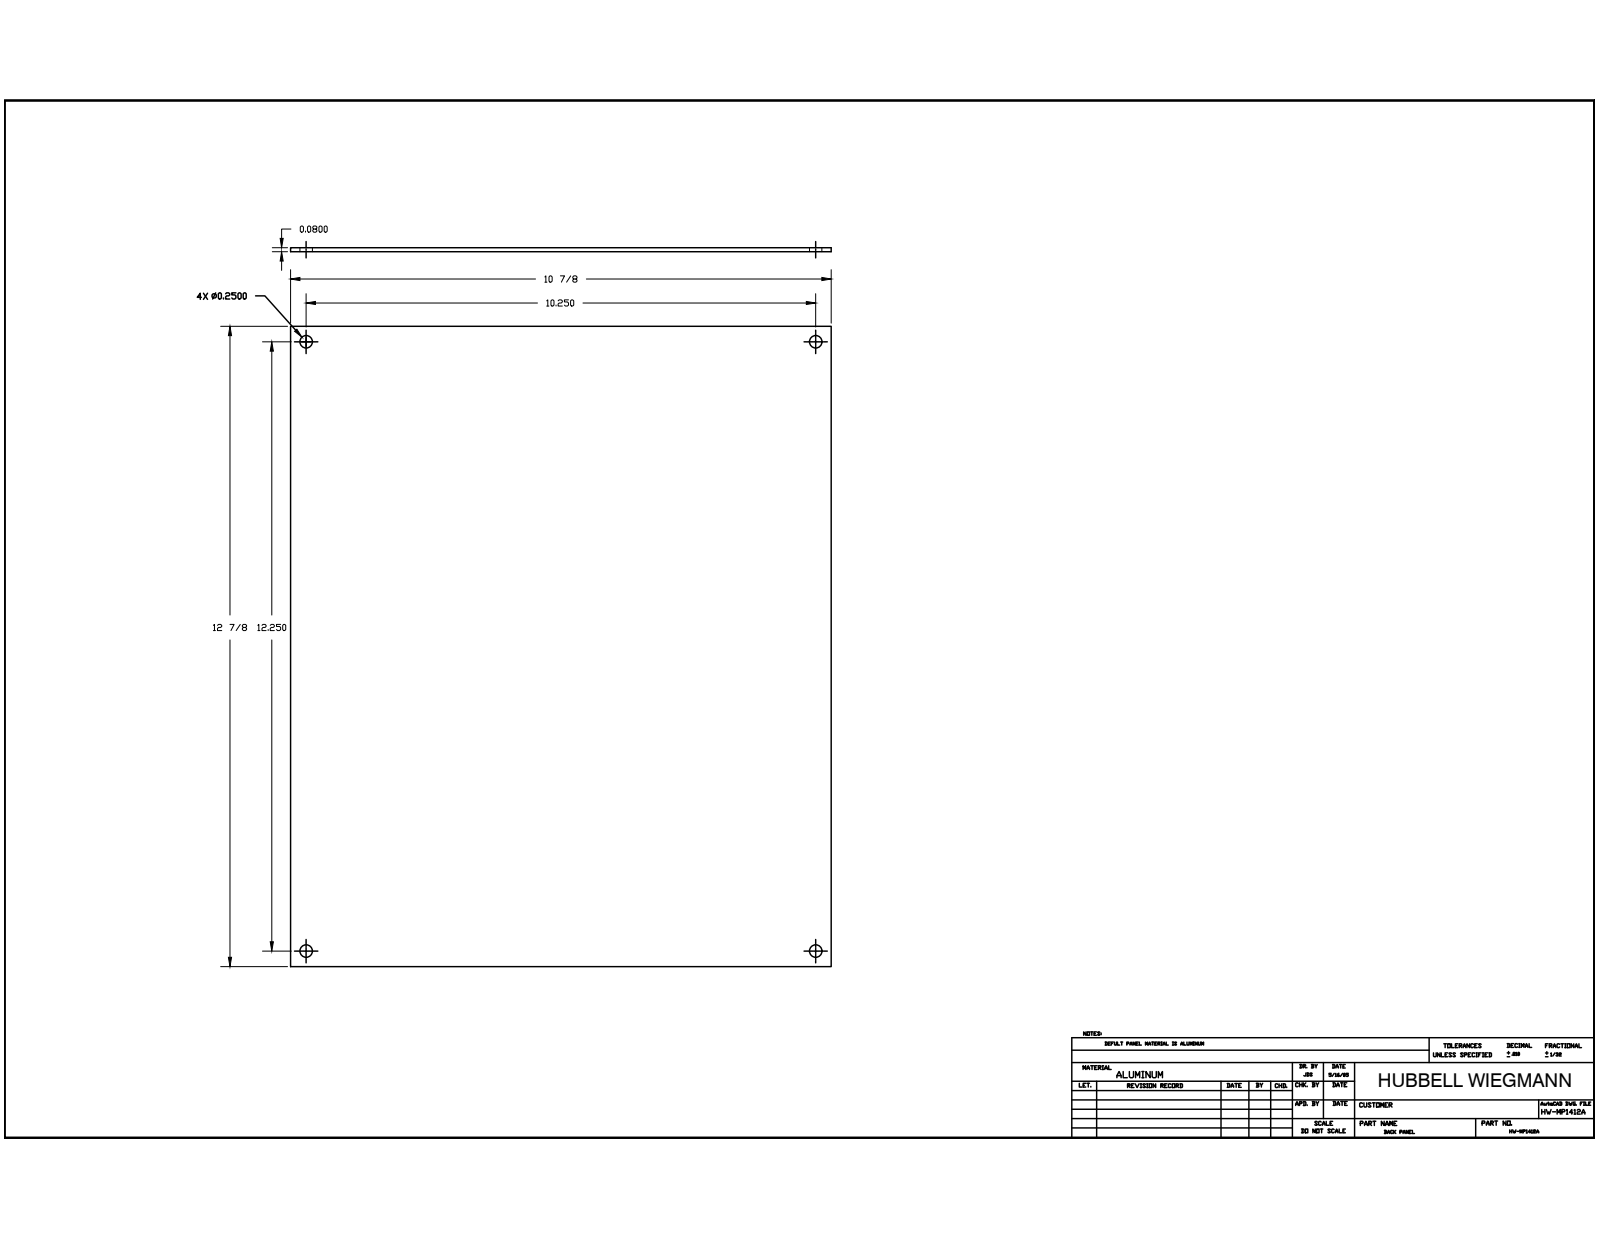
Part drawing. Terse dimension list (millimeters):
name: BP1412AL_STP
written by: Autodesk Inventor 2014 (AUTOMOTIVE_DESIGN)
unit: mm
bodies: 1 solid, 10 faces (6 planar, 4 cylindrical, 0 other)
size: 327.02 × 276.23 × 2.03
volume: 183 298 mm³; area: 183 025 mm²
holes: 4× ⌀6.35
face distances: 2.03, 276.22, 327.02
hole spacings: 260.34, 311.14, 405.69
